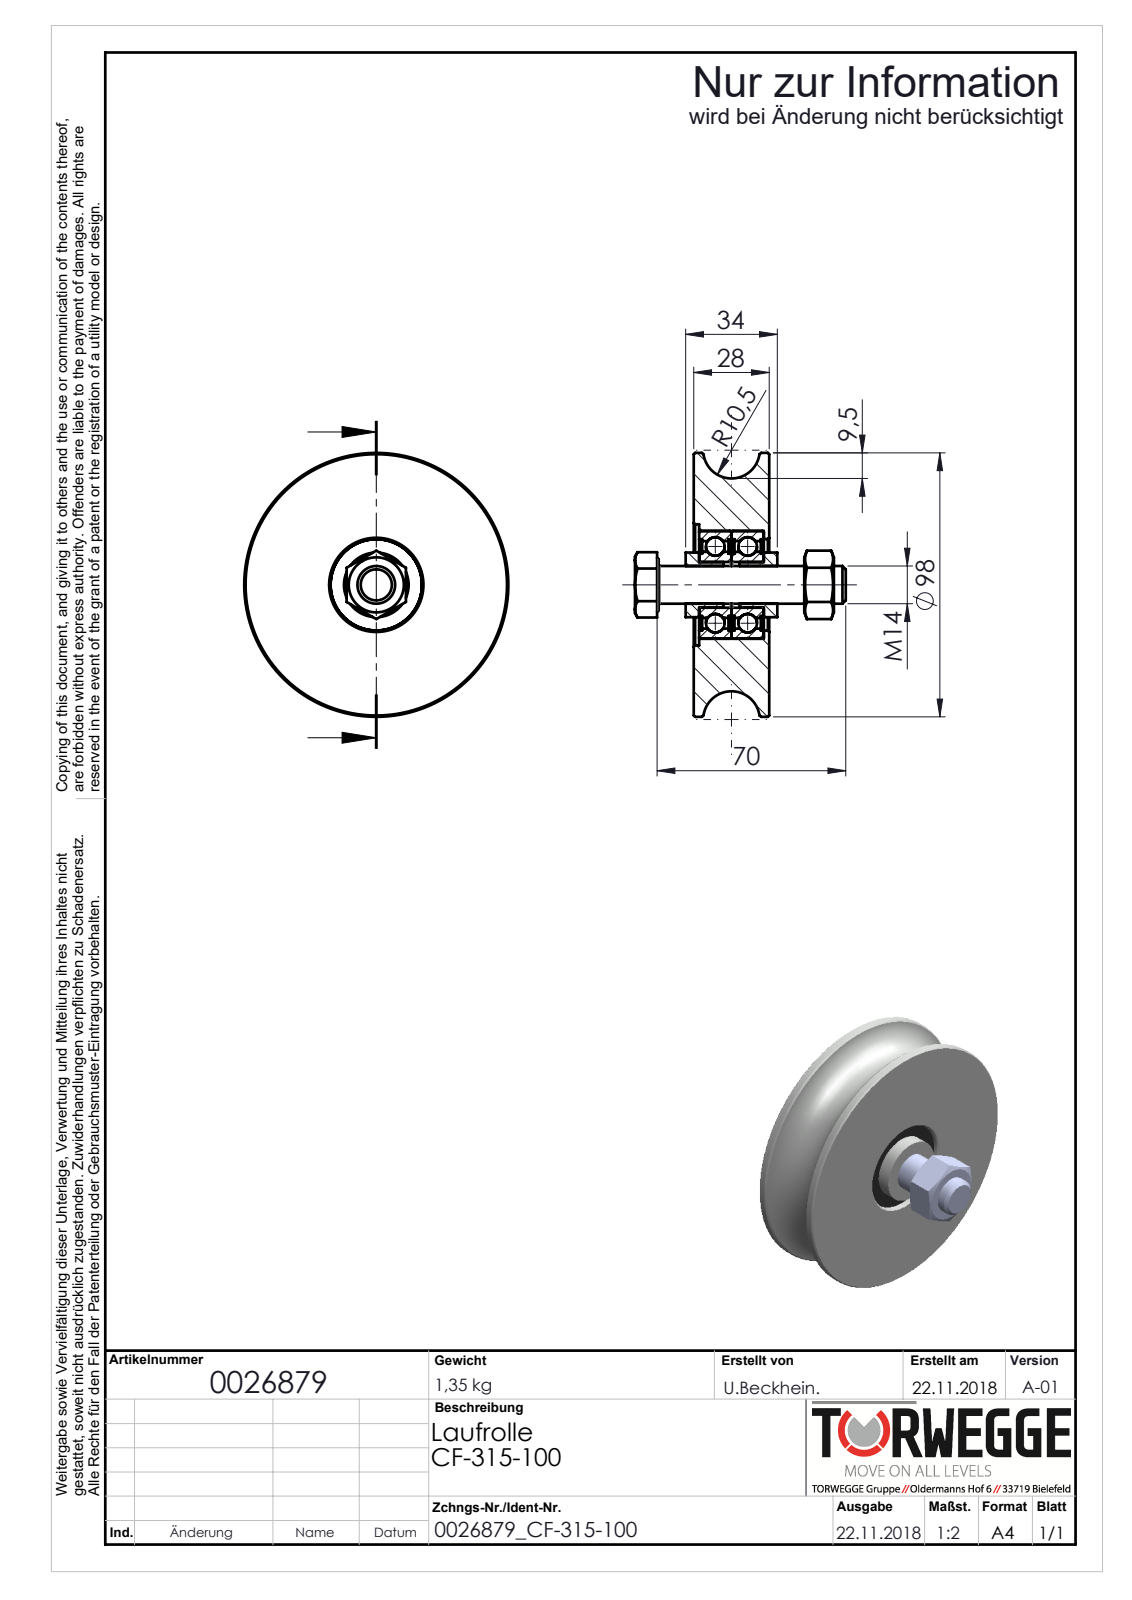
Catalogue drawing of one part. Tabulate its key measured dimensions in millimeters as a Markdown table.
| quantity | value |
| --- | --- |
| part name | 0026879_CF-315-100_(A-01) |
| STEP written by | SolidWorks 2018 (AUTOMOTIVE_DESIGN) |
| units | millimeters |
| bodies | 15 solids, 208 faces (52 planar, 82 cylindrical, 74 other) |
| overall size | 98 × 98 × 78.2 |
| volume | 175 550 mm³ |
| surface area | 56 751 mm² |
| round holes (diameter × count) | 11.84 × 1, 14 × 1, 17 × 1, 23.1 × 1, 32.5 × 1, 33.91 × 1, 34 × 1, 45 × 1 |
| round bosses / shafts (diameter × count) | 98 × 1, 40 × 1, 24.5 × 1, 24 × 1, 16.9 × 1 |
| main face-to-face distances | 28, 12, 14, 26, 2, 0.56, 11.44, 24, 10.88, 12.56 |
